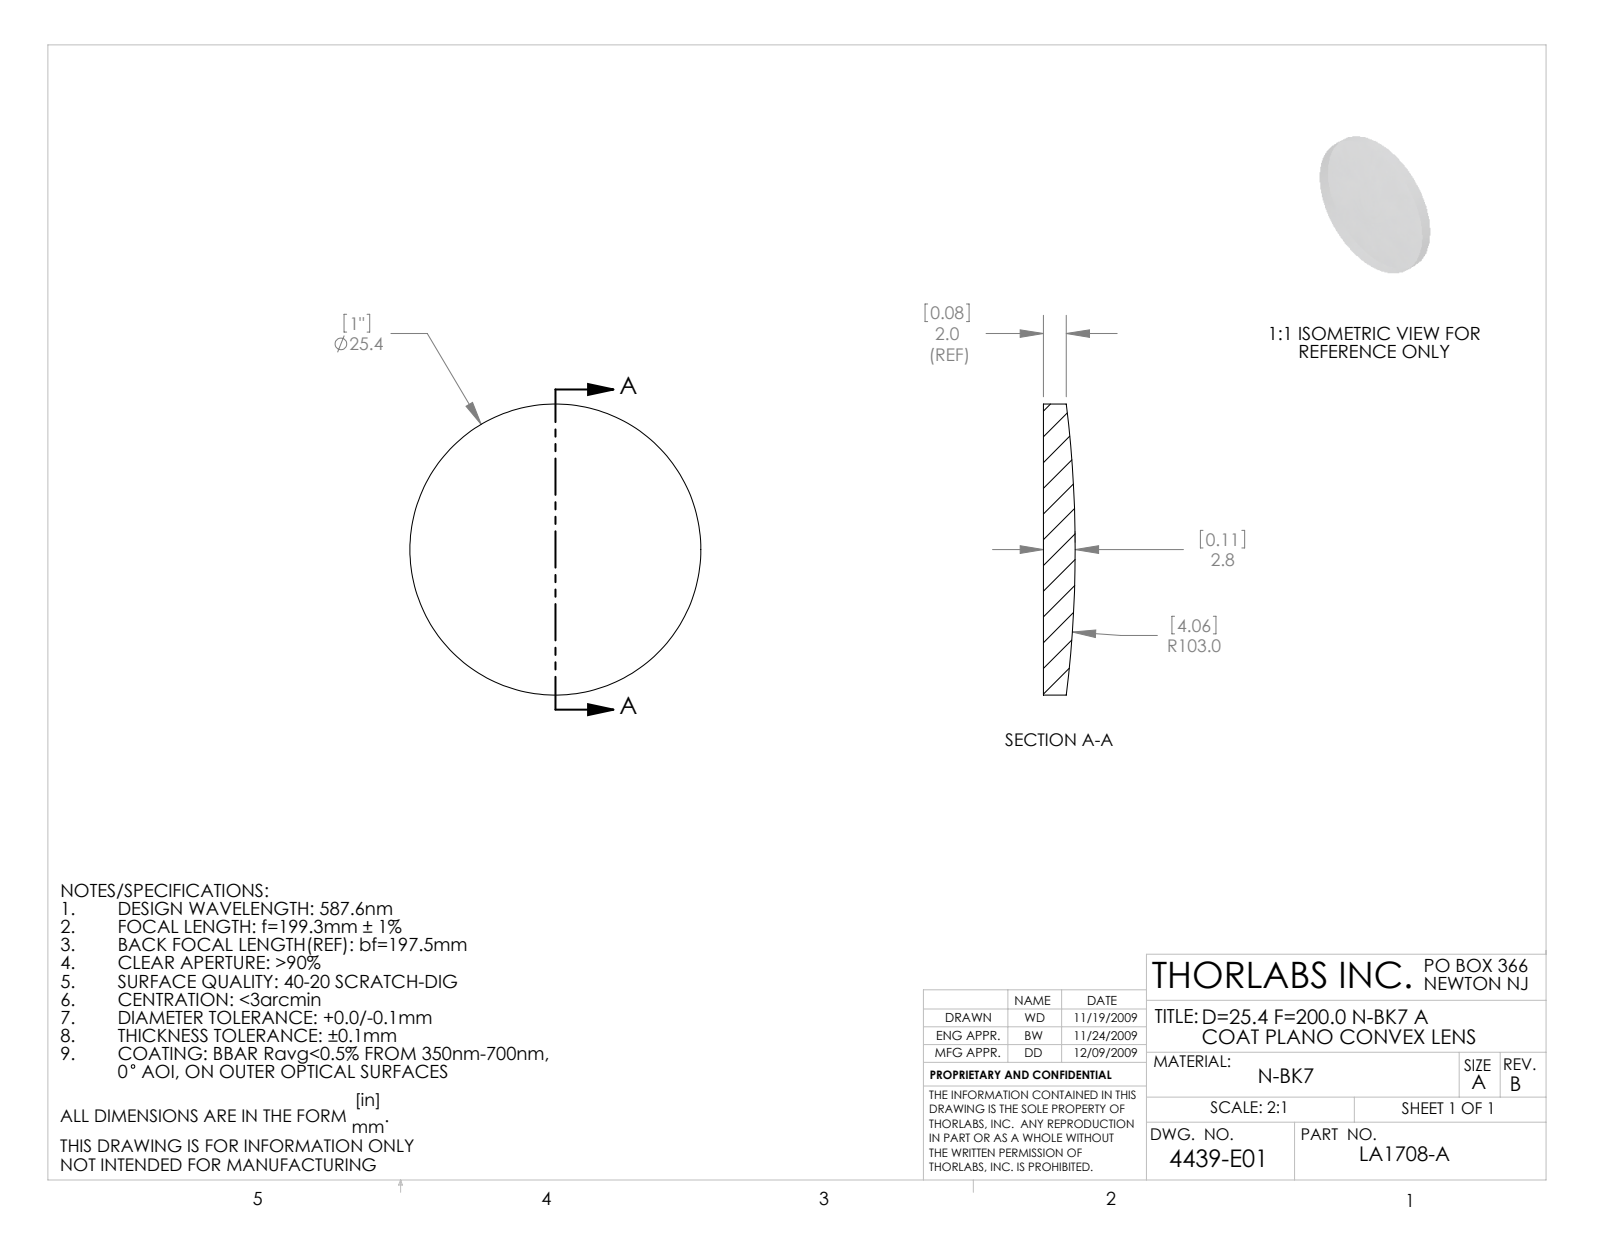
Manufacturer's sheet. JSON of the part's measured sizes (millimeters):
{"part_name": "4439-E0W", "step_written_by": "SolidWorks 2009 (AUTOMOTIVE_DESIGN)", "units": "millimeters", "bodies": {"solids": 1, "faces": 5, "planar": 1, "cylindrical": 2, "other": 2}, "overall_size": [25.4, 25.4, 2.78], "volume_mm3": 1210, "surface_area_mm2": 1174, "round_bosses_or_shafts": [[25.4, 1]]}
